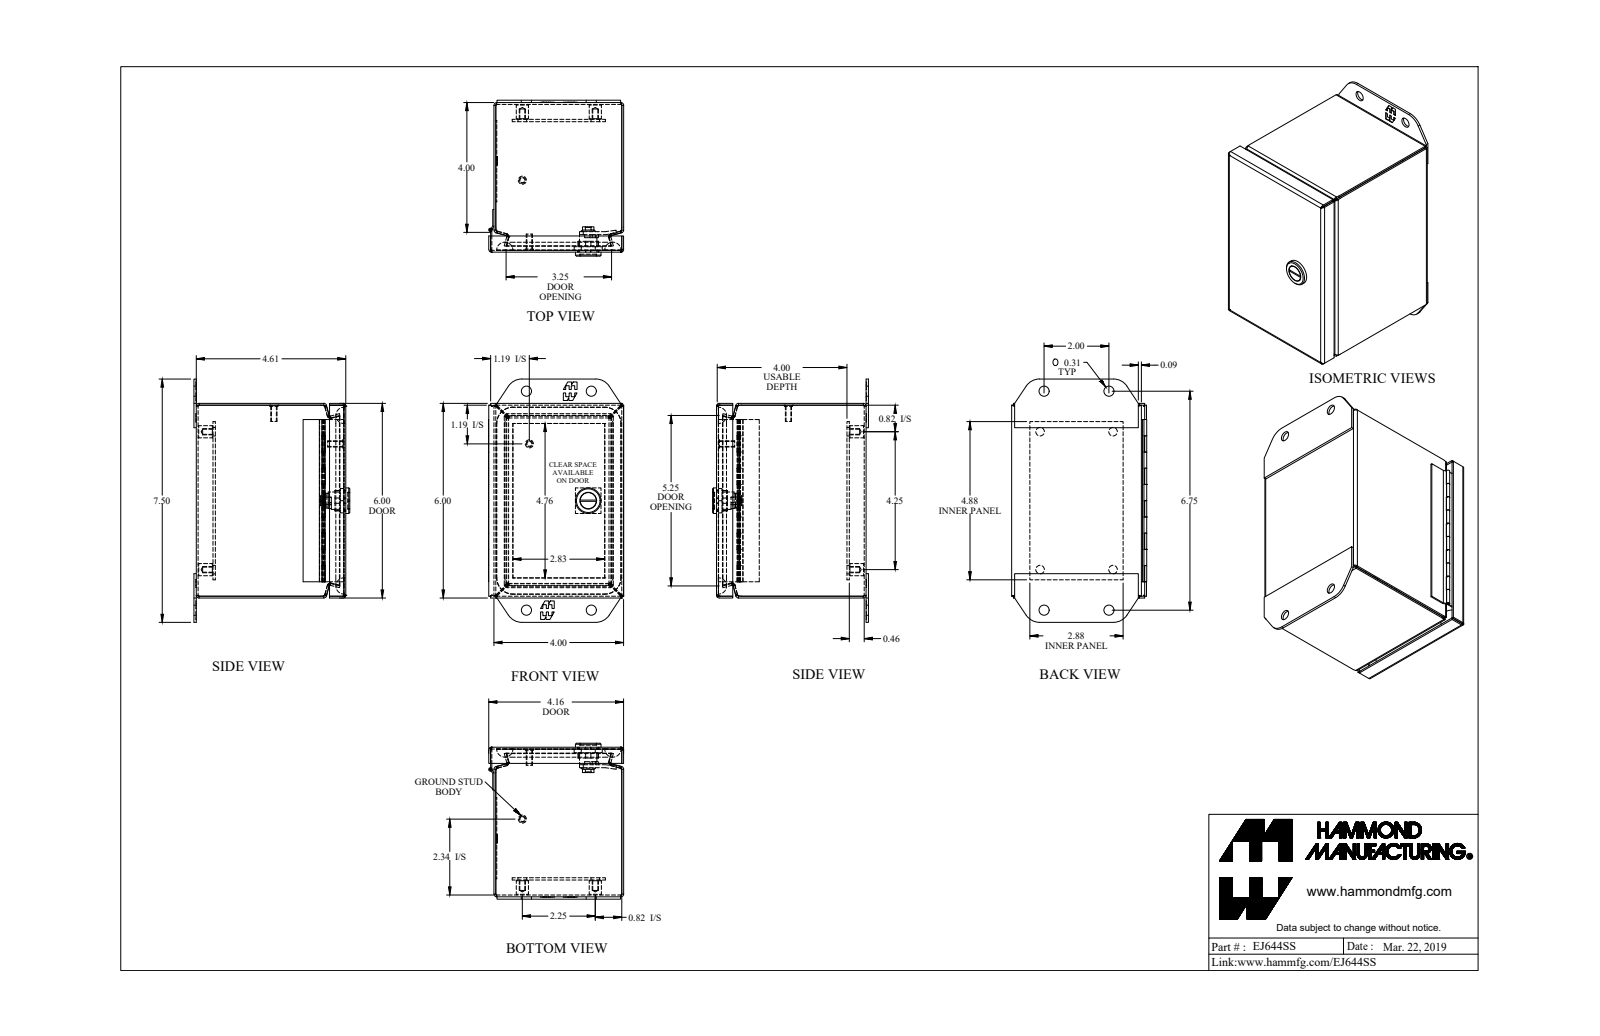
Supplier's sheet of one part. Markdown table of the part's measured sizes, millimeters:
| quantity | value |
| --- | --- |
| part name | EJ644SS_Default |
| STEP written by | SolidWorks 2019 (CONFIG_CONTROL_DESIGN) |
| units | millimeters |
| bodies | 16 solids, 624 faces (354 planar, 174 cylindrical, 96 other) |
| overall size | 190.5 × 122 × 105.8 |
| volume | 203 400 mm³ |
| surface area | 264 600 mm² |
| round holes (diameter × count) | 4 × 4, 6.7 × 4, 8 × 4, 1.3 × 1, 13.1 × 1 |
| round bosses / shafts (diameter × count) | 9.5 × 4, 6.4 × 2, 4.8 × 2, 20 × 1, 13.6 × 1, 12.6 × 1, 11 × 1, 2.5 × 1 |
| partial cylindrical surfaces (radius × count) | 0.7 × 16, 2.2 × 16, 7.1 × 12, 6.4 × 4, 12.7 × 4, 12.7 × 4, 1.5 × 2, 0.8 × 1 |
| main face-to-face distances | 1.4, 115.7, 100.2, 151, 1.8, 15, 117.1, 98.7, 114.2, 101.6 |
| hole center spacings | 31.9, 139.8, 108, 62.6, 74.7, 149.8, 50.8, 54.3 |
